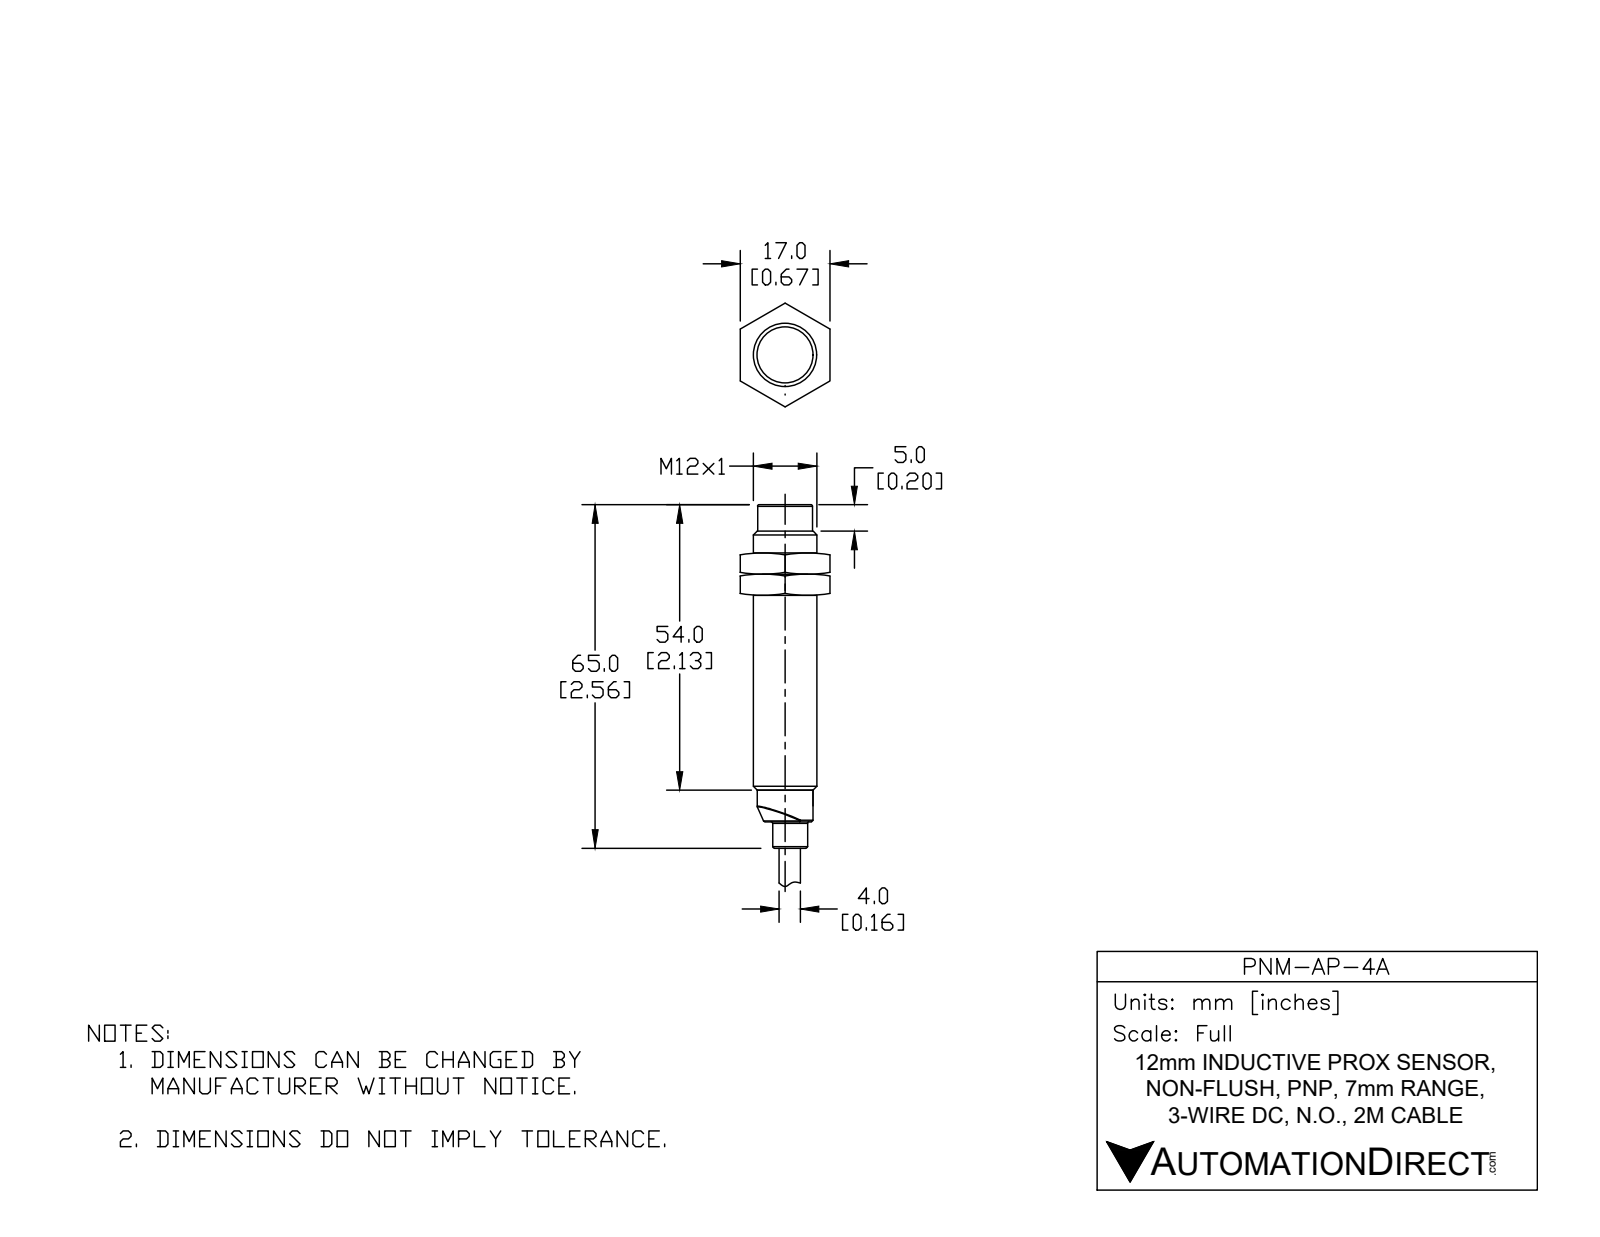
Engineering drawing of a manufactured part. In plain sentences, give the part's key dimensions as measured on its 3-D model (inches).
The part is named "PNM-AP-4A". Its 3-D file was written by "SolidWorks 2017 (AUTOMOTIVE_DESIGN)". It is 1 solid with 68 faces: 21 planar, 19 cylindrical and 28 other. Overall it measures 4.559 by 0.472 by 0.472 inches. Its volume is 0.452 cubic inches and its surface area 4.972 square inches. Round holes: 1 of diameter 0.161, 1 of diameter 0.401. Round bosses or shafts: 1 of diameter 0.472, 1 of diameter 0.417, 1 of diameter 0.415, 1 of diameter 0.384, 1 of diameter 0.26, 1 of diameter 0.157. Partial cylindrical surfaces (rounded edges, fillets, slot ends): 1 of radius 0.091. The main face-to-face distances are 2.362, 2.559, 0.197, 4.559, 2.197, 2, 0.022, 2.34, 2.537, 4.537. The hole center spacings are 0.039.
